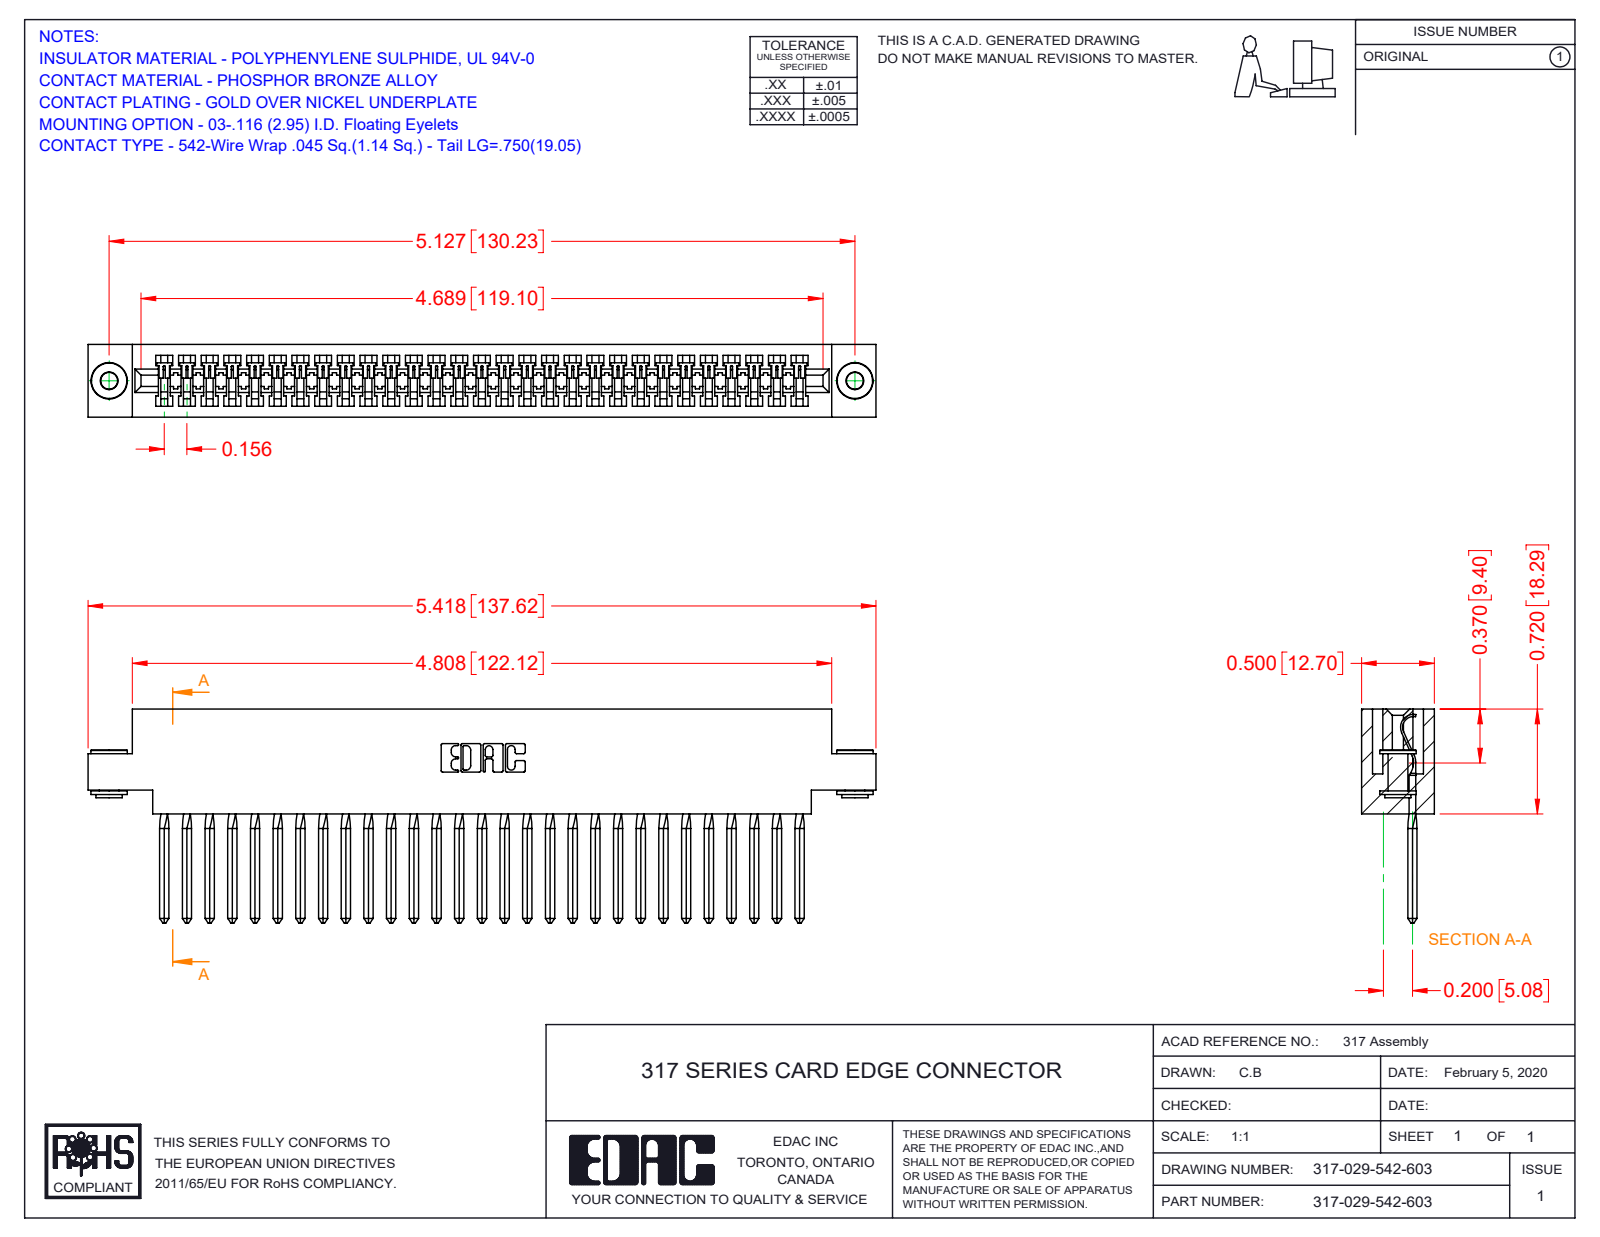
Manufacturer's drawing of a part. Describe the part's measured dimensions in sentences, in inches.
The part is named "317-290-003_542; 317 Part_.156 Dia - TH; 317-029-542-603; 345-250-002_345-250-002-102". Its 3-D file was written by "SolidWorks 2016 (CONFIG_CONTROL_DESIGN)". It is 32 solids with 2315 faces: 1924 planar, 267 cylindrical and 124 other. Overall it measures 5.418 by 1.47 by 0.5 inches. Its volume is 1.277 cubic inches and its surface area 39.47 square inches. Round holes: 2 of diameter 0.116, 2 of diameter 0.156. Round bosses or shafts: 2 of diameter 0.25, 2 of diameter 0.18, 2 of diameter 0.136. Partial cylindrical surfaces (rounded edges, fillets, slot ends): 58 of radius 0.006, 22 of radius 0.01, 6 of radius 0.007, 6 of radius 0.031, 3 of radius 0.026, 1 of radius 0.074, 1 of radius 0.089, 1 of radius 0.1. The main face-to-face distances are 0.5, 0.075, 0.425, 0.35, 0.11, 0.72, 0.136, 0.211, 0.289, 0.213. The hole center spacings are 5.127.
